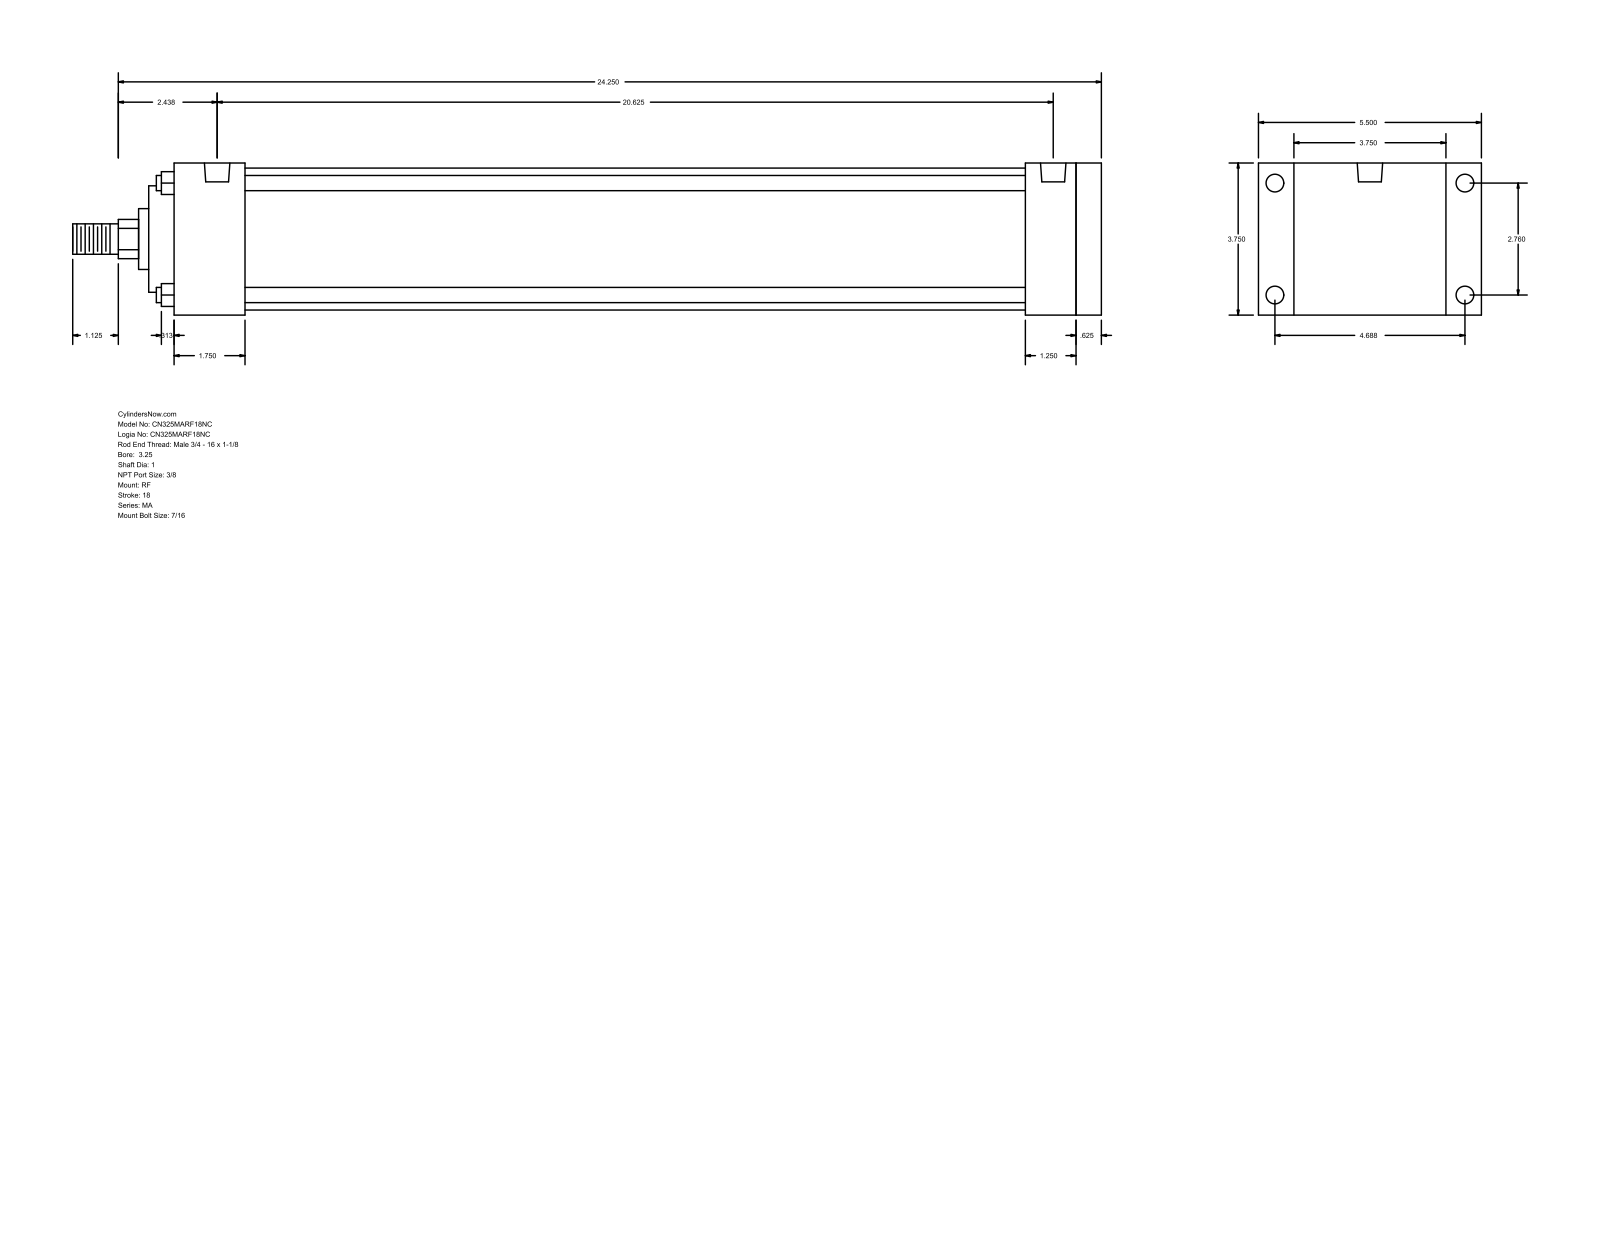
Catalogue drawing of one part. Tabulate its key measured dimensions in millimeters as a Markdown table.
| quantity | value |
| --- | --- |
| part name | MA_RF__0325_1 |
| STEP written by | GSSL Pune (CONFIG_CONTROL_DESIGN) |
| units | millimeters |
| bodies | 0 solids, 94 faces (65 planar, 29 cylindrical, 0 other) |
| overall size | 644.52 × 139.7 × 95.25 |
| round holes (diameter × count) | 11.11 × 8, 15.93 × 2 |
| round bosses / shafts (diameter × count) | 9.53 × 4, 88.9 × 1, 66.67 × 1, 38.1 × 1, 25.4 × 1, 19.05 × 1 |
| partial cylindrical surfaces (radius × count) | 12.29 × 1 |
| main face-to-face distances | 95.24, 581.03, 15.87, 565.16, 22.23, 117.47, 47.62, 596.9, 533.41, 31.75 |
| hole center spacings | 70.1, 119.06, 138.16, 514.35, 4.76, 4.77, 519.11, 519.12 |
